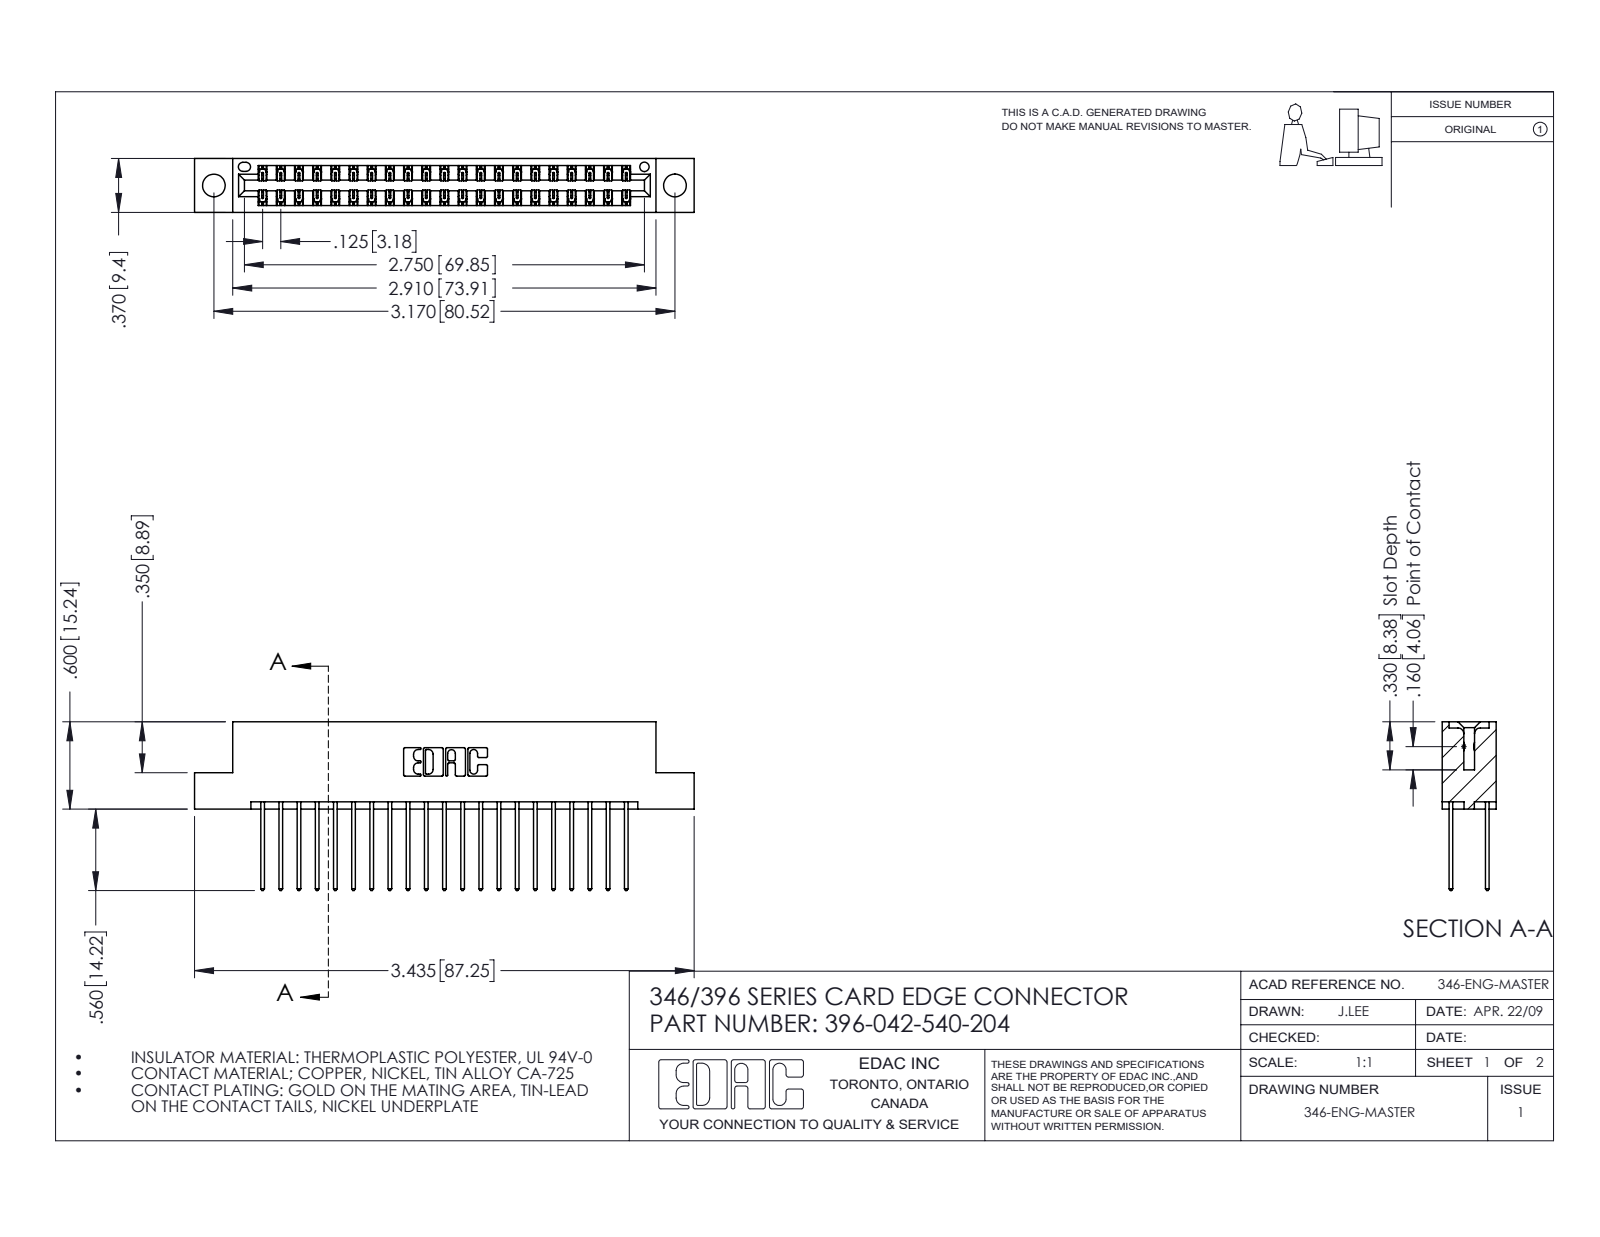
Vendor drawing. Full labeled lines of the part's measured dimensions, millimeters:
Part name (STEP PRODUCT): 346 Part_Flush Mounting Lugs - 0.156 Dia-TH; 396-042-540-204; 345-292-001_345-293-140
STEP written by: SolidWorks 2016 (CONFIG_CONTROL_DESIGN)
Units: millimetres
Bodies: 43 solids, 2306 faces (1546 planar, 760 cylindrical, 0 other)
Overall size (bounding box): 87.2 × 29.5 × 9.4
Volume: 8 420 mm³ · Surface area: 11 810 mm²
Round holes (diameter × count): ⌀4 ×2, ⌀1.6 ×1
Partial cylindrical surfaces — rounded edges, fillets, slot ends (radius × count): R0.2 ×63, R0.3 ×42, R0.3 ×22, R0.2 ×6, R0.8 ×6, R0.7 ×3, R0.4 ×2, R0.6 ×2
Main face-to-face distances: 1.2, 8.2, 6.4, 9.4, 1.8, 7.6, 0.6, 7, 3.8, 5.6
Hole centre spacings: 6.2, 75.3, 80.5
